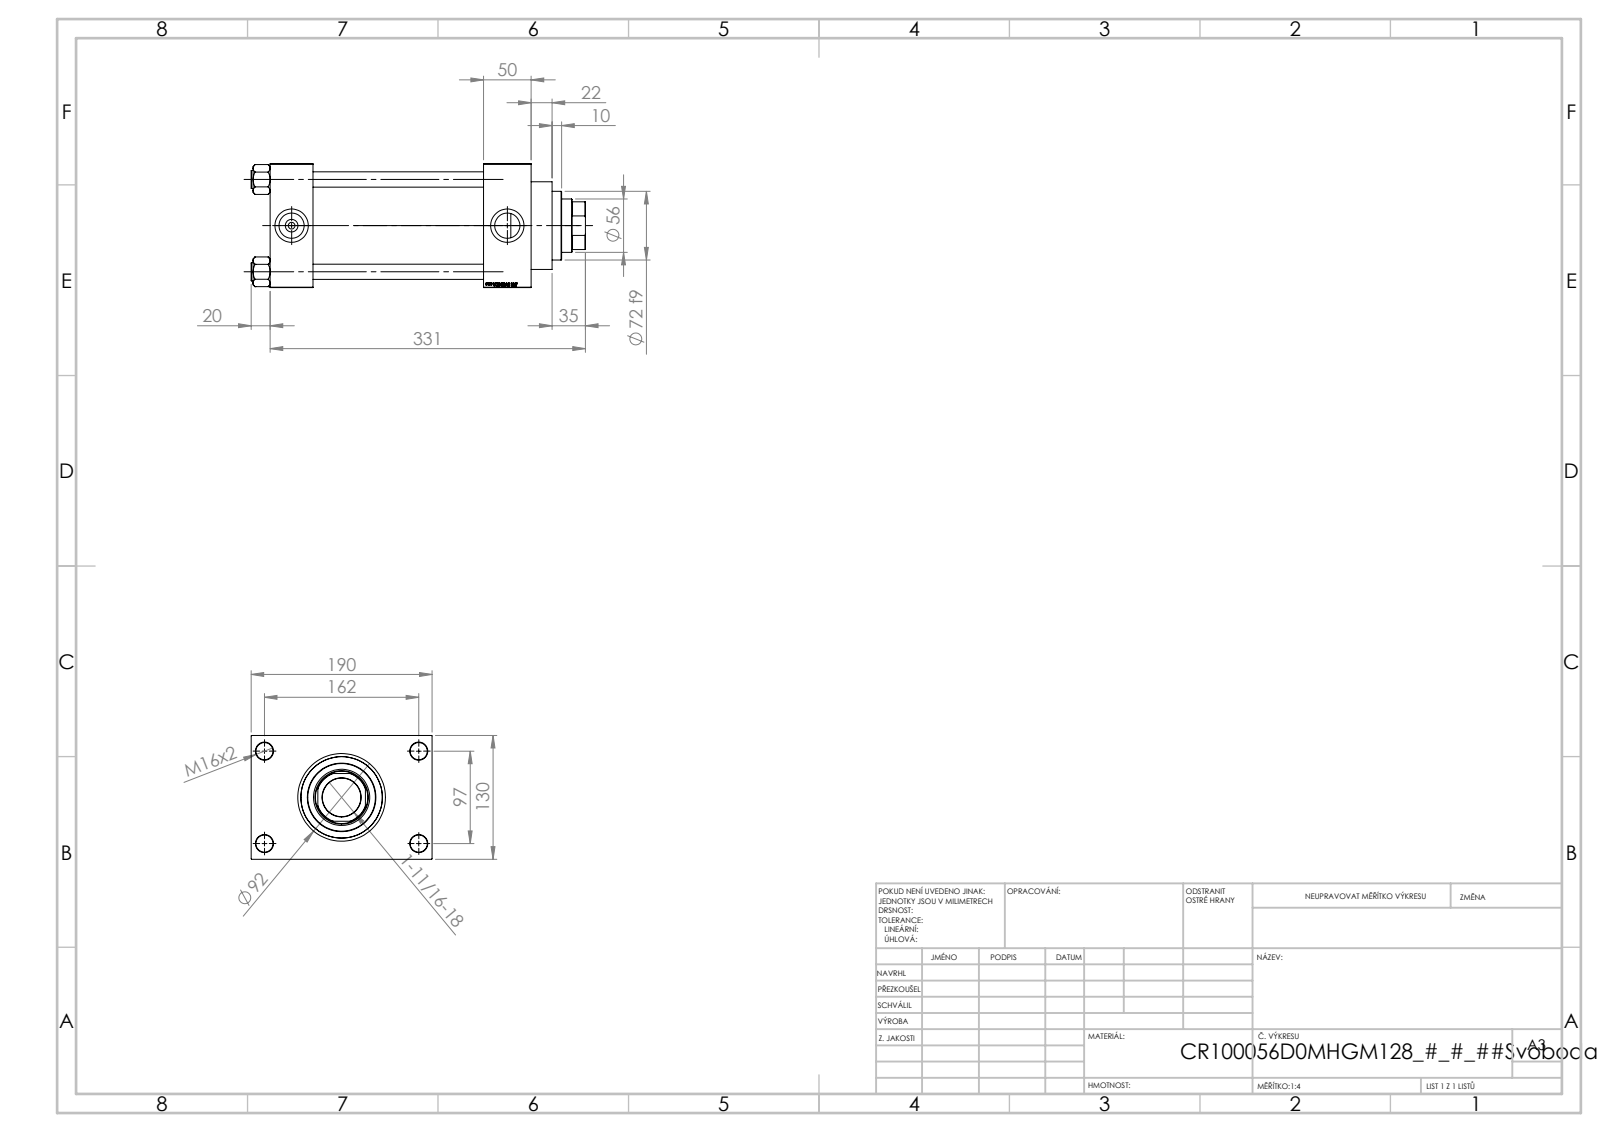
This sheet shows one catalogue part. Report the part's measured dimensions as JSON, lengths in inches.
{"part_name": "V215CR_D_Body; NUT_M5_D; V215CR_D_TYCINKA; V215_VC_A (+1 more)", "step_written_by": "SolidWorks 2019 (CONFIG_CONTROL_DESIGN)", "units": "inches", "bodies": {"solids": 11, "faces": 1151, "planar": 545, "cylindrical": 88, "other": 518}, "overall_size": [13.819, 7.48, 5.118], "volume_in3": 188.3, "surface_area_in2": 733.1, "round_holes": [[0.63, 4], [0.709, 4], [0.276, 2], [1.041, 2], [1.378, 2], [1.594, 1], [2.205, 1], [2.323, 1], [2.992, 1], [3.366, 1], [3.937, 1]], "round_bosses_or_shafts": [[0.748, 4], [4.173, 1], [3.622, 1], [2.835, 1]], "partial_cylinders_radius": [[1.063, 1]], "face_to_face_distances": [5.118, 1.969, 1.772, 8.819, 7.047, 10.787, 9.016, 1.181, 6.299, 5.039], "hole_center_spacings": [1.281, 2.698, 3.717, 3.815, 4.026, 5.096, 6.367, 3.819]}
